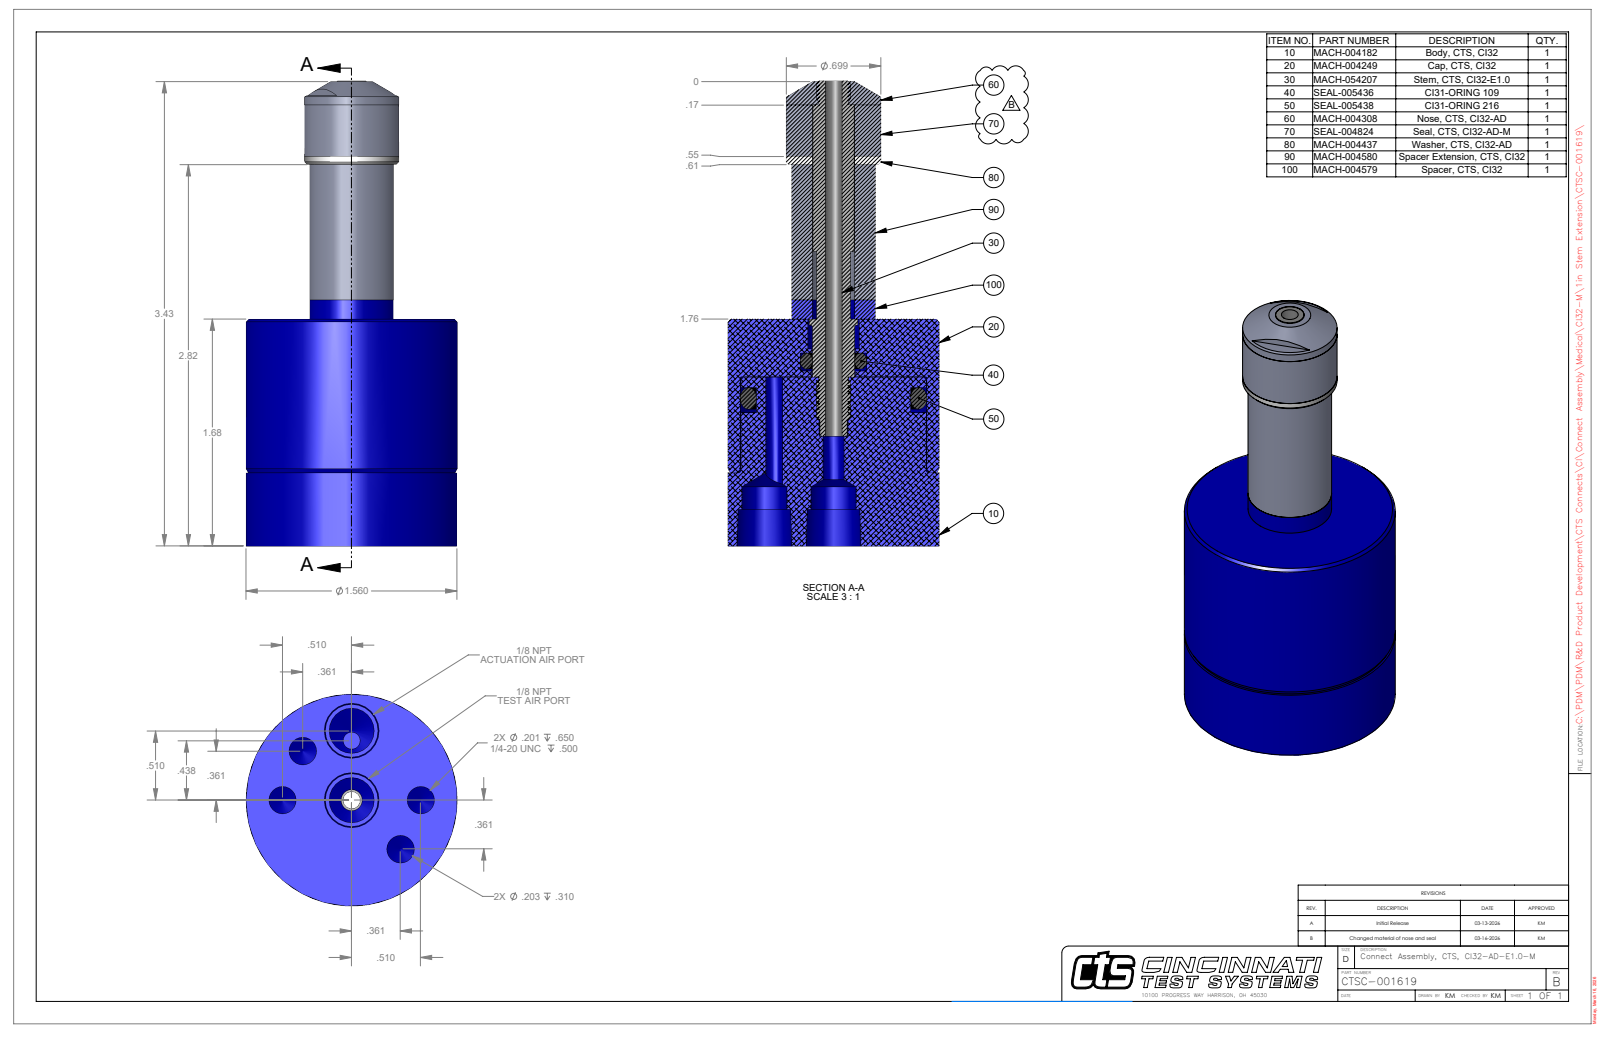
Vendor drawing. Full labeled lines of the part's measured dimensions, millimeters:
Part name (STEP PRODUCT): CTSC-001619
STEP written by: SolidWorks 2023 (AUTOMOTIVE_DESIGN)
Units: millimetres
Bodies: 6 solids, 71 faces (31 planar, 25 cylindrical, 15 other)
Overall size (bounding box): 87.3 × 39.62 × 39.62
Volume: 58 300 mm³ · Surface area: 16 035 mm²
Round holes (diameter × count): ⌀5.11 ×2, ⌀5.16 ×2, ⌀8.43 ×2, ⌀3.17 ×1, ⌀3.97 ×1, ⌀5.41 ×1, ⌀7.87 ×1, ⌀7.99 ×1, ⌀9.65 ×1
Round bosses / shafts (diameter × count): ⌀39.62 ×1, ⌀17.75 ×1, ⌀15.7 ×1, ⌀9.08 ×1, ⌀7.72 ×1, ⌀6.35 ×1
Partial cylindrical surfaces — rounded edges, fillets, slot ends (radius × count): R1.59 ×1
Main face-to-face distances: 42.6, 82.77, 40.17, 73.12, 30.52, 9.65, 71.59, 28.99, 1.53, 11.18
Hole centre spacings: 12.95, 9.91, 23.93, 18.31, 25.9, 25.91
